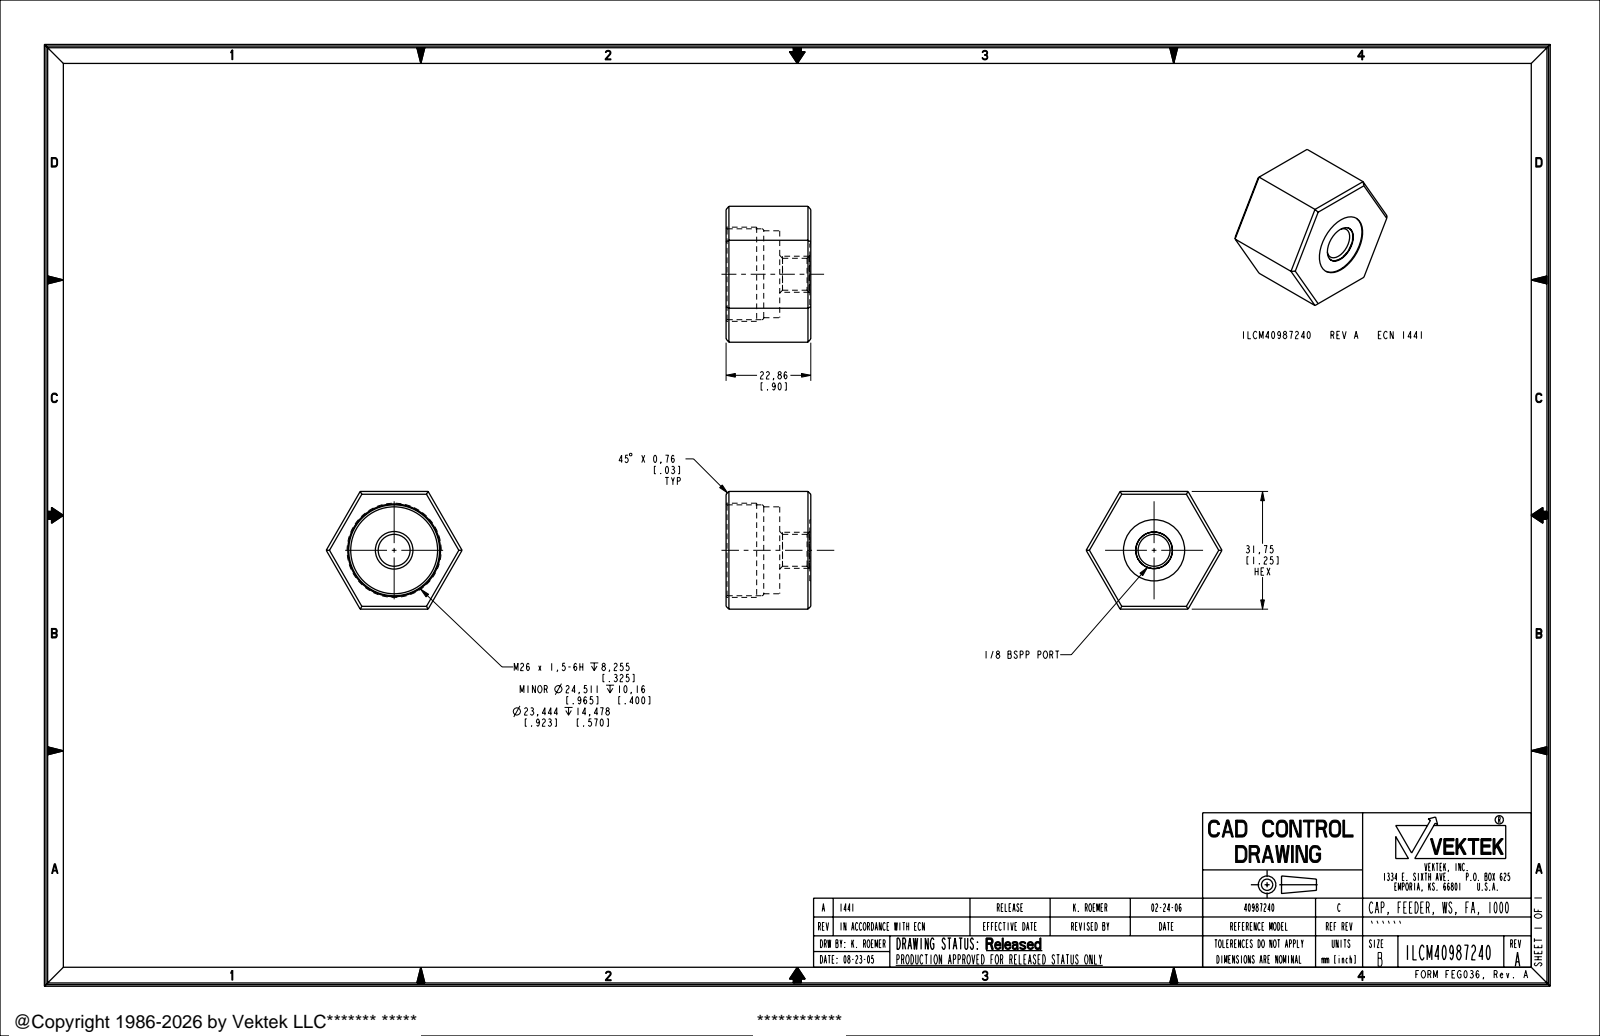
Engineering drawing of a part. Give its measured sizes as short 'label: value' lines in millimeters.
name: ILCM40987240
written by: PRO/ENGINEER BY PARAMETRIC TECHNOLOGY CORPORATION, 2004290 (AUTOMOTIVE_DESIGN_CC2)
unit: mm
bodies: 1 solid, 47 faces (25 planar, 12 cylindrical, 10 other)
size: 36.66 × 31.75 × 22.86
volume: 12 694 mm³; area: 6 258 mm²
holes: 1× ⌀8.61, 1× ⌀16.51, 1× ⌀23.44, 1× ⌀24.51
bosses: 1× ⌀25.4, 1× ⌀9.73
face distances: 31.74, 31.76, 8.38, 14.48, 22.86, 22.61, 8.13, 37.52, 37.53, 37.54
